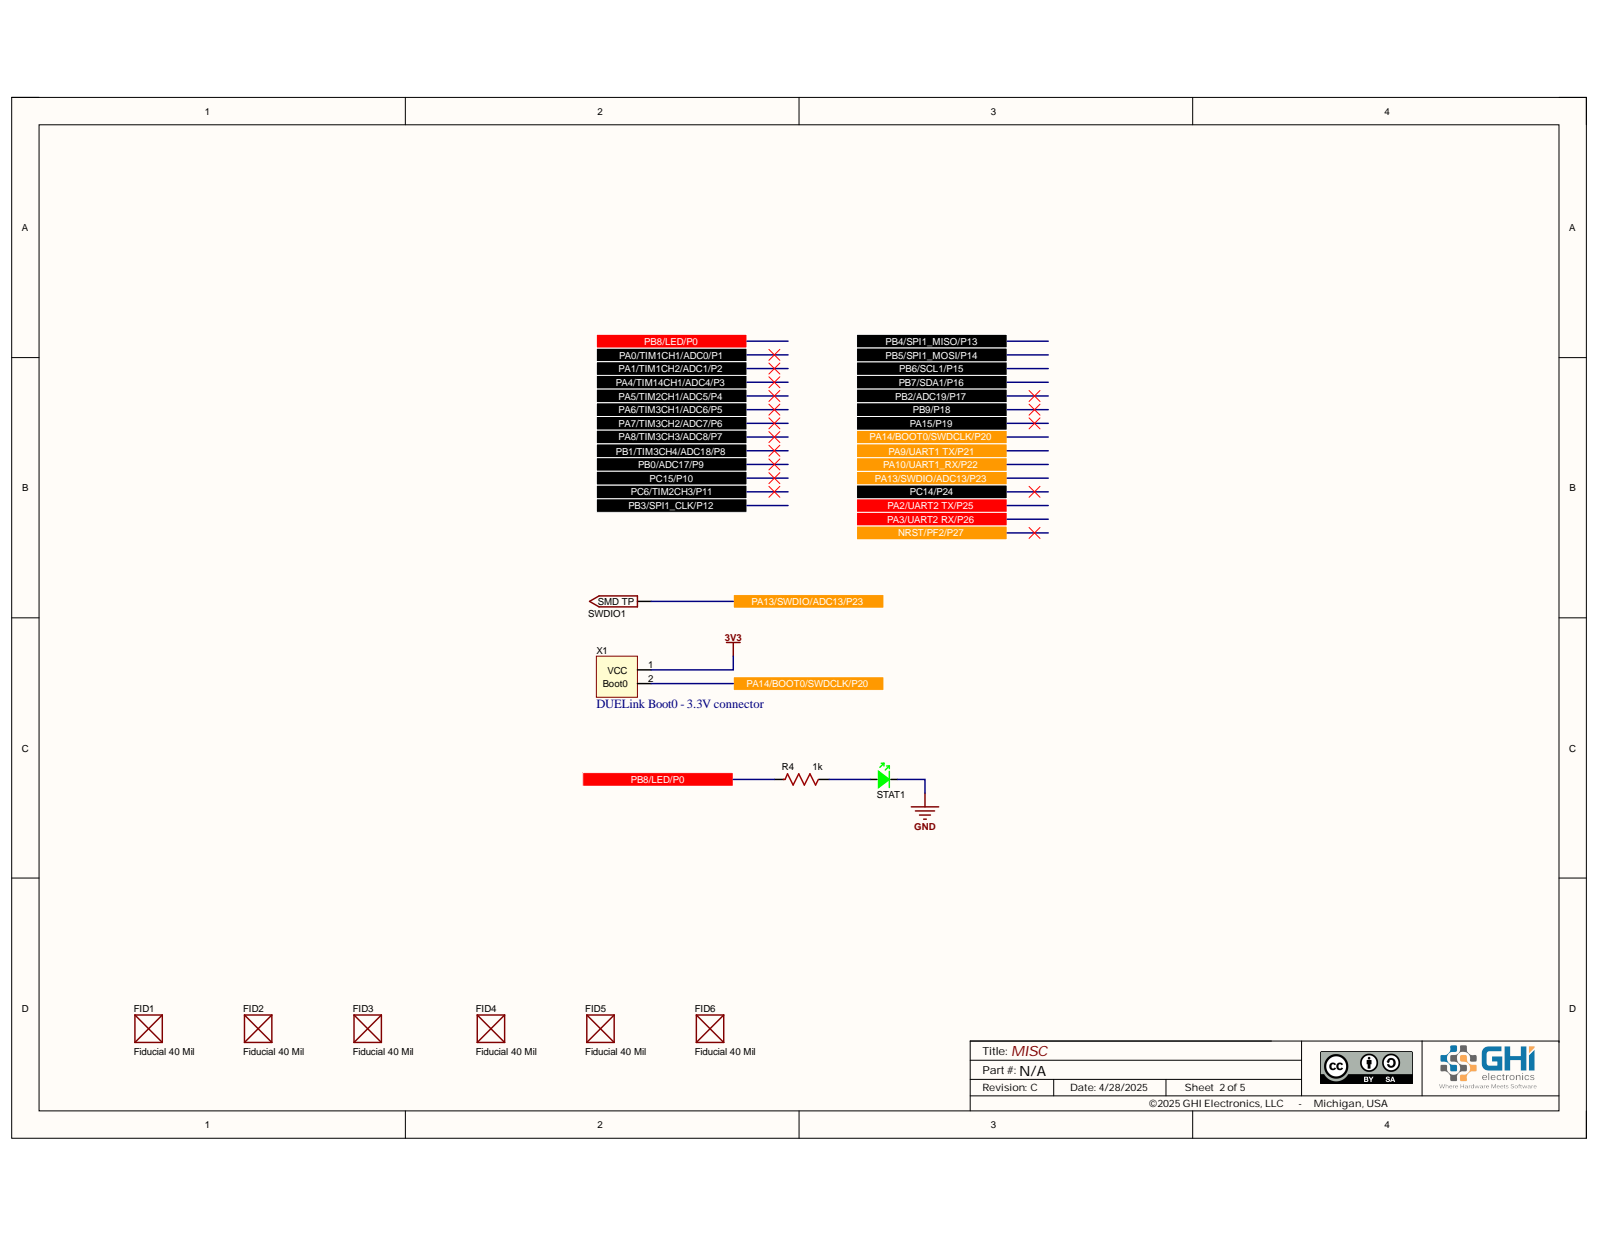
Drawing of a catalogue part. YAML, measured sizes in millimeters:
part_name: "PCB; Board; R3; User Library-R SMD 0402 (+7 more)"
step_written_by: "Open CASCADE 7.5 (AUTOMOTIVE_DESIGN)"
units: millimeters
bodies: {solids: 124, faces: 2506, planar: 1589, cylindrical: 570, other: 347}
overall_size: [25, 22, 14.92]
volume: 1772
surface_area: 3134
round_holes:
  - {diameter: 1.02, count: 8}
  - {diameter: 1.02, count: 2}
  - {diameter: 3, count: 2}
partial_cylinders:
  - {radius: 0.12, count: 35}
  - {radius: 0.15, count: 14}
  - {radius: 0.17, count: 2}
  - {radius: 0.18, count: 2}
  - {radius: 0.18, count: 2}
  - {radius: 1, count: 2}
  - {radius: 3.5, count: 2}
face_to_face_distances: [1.6, 5, 2, 3, 6.6, 4.6, 2.54, 0.64, 22, 0.68]
hole_center_spacings: [2.54, 5.08, 7.62, 10.16, 12.7, 5.62, 5.67, 6.62]
